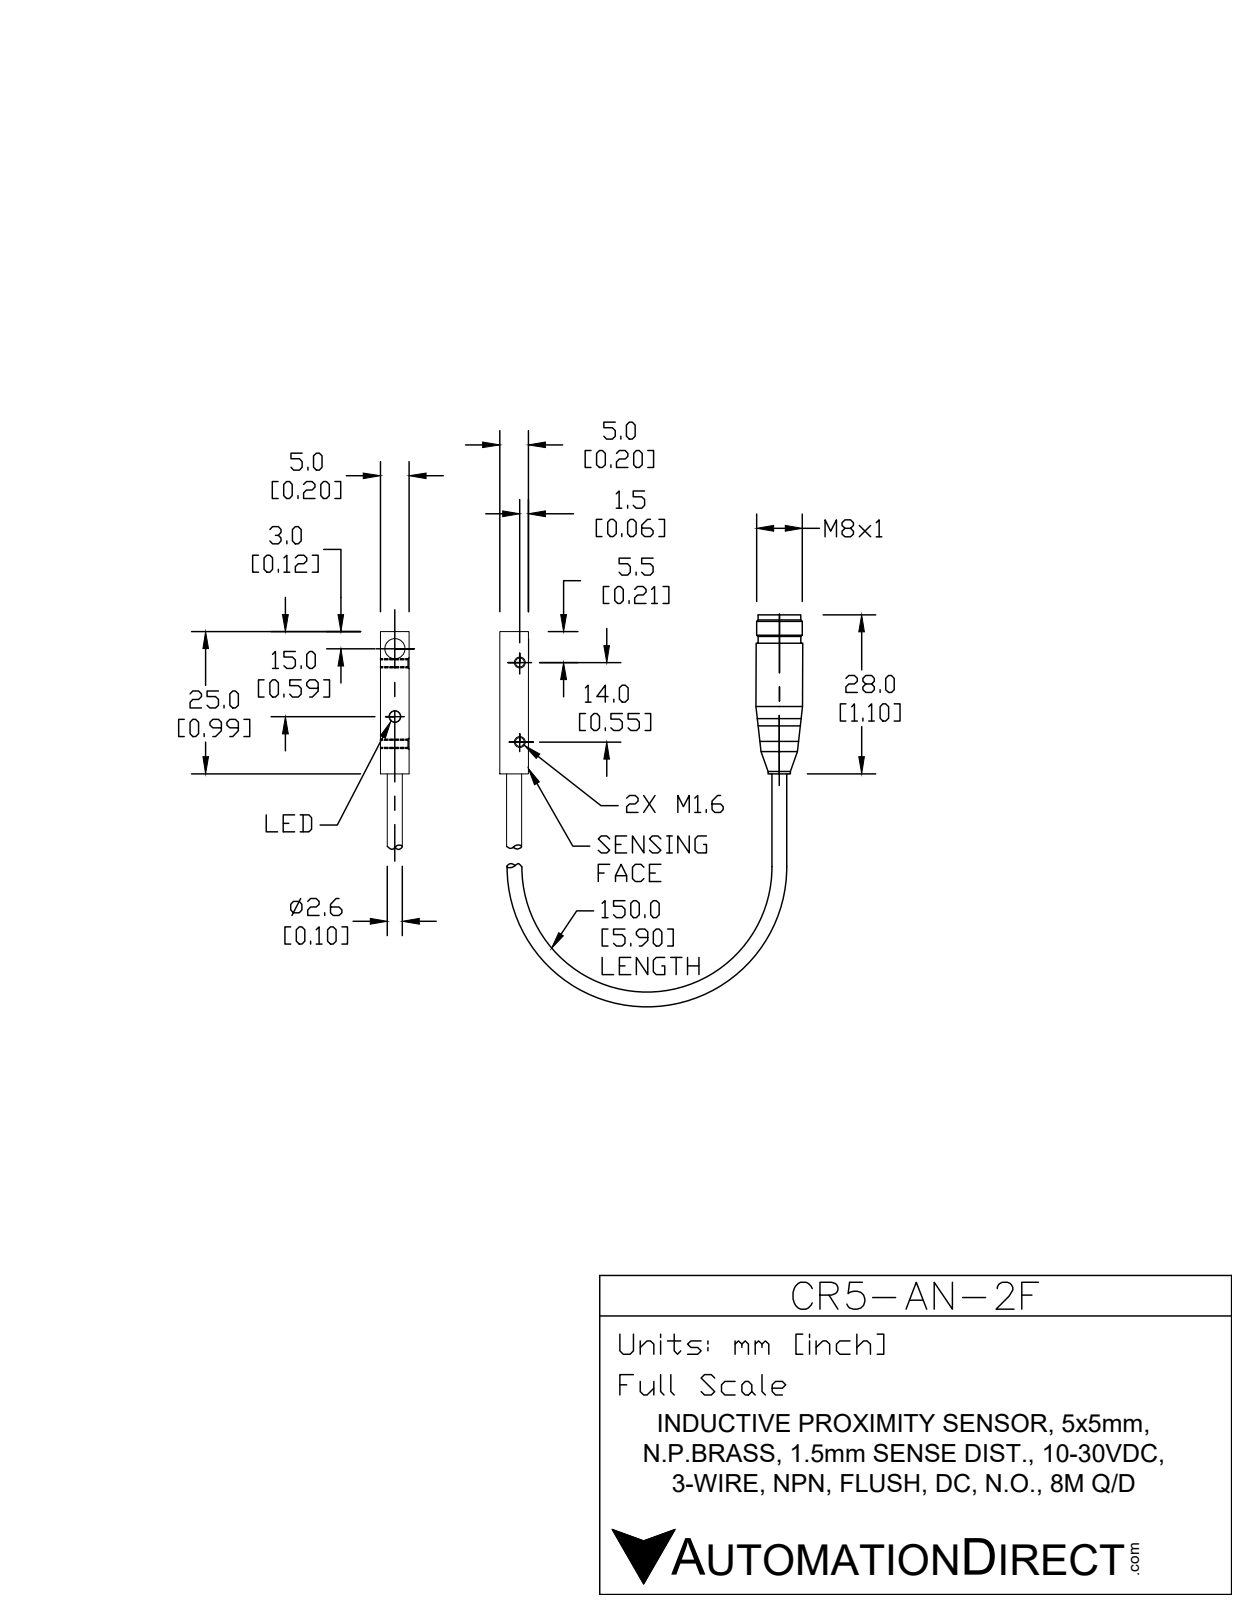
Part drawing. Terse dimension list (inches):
name: CR5-AN-2F
written by: SolidWorks 2017 (AUTOMOTIVE_DESIGN)
unit: in
bodies: 2 solids, 359 faces (127 planar, 84 cylindrical, 148 other)
size: 3.732 × 0.393 × 0.393
volume: 0.158 in³; area: 3.343 in²
holes: 2× ⌀0.049, 1× ⌀0.228
bosses: 3× ⌀0.039, 1× ⌀0.386, 1× ⌀0.315, 1× ⌀0.295, 1× ⌀0.272, 1× ⌀0.256, 1× ⌀0.102
rounds: 8× R0.008, 1× R0.197
face distances: 0.197, 0.035, 0.071, 0.106, 2.362, 0.256, 1.173, 3.535, 2.551, 1.378
hole spacings: 0.551
